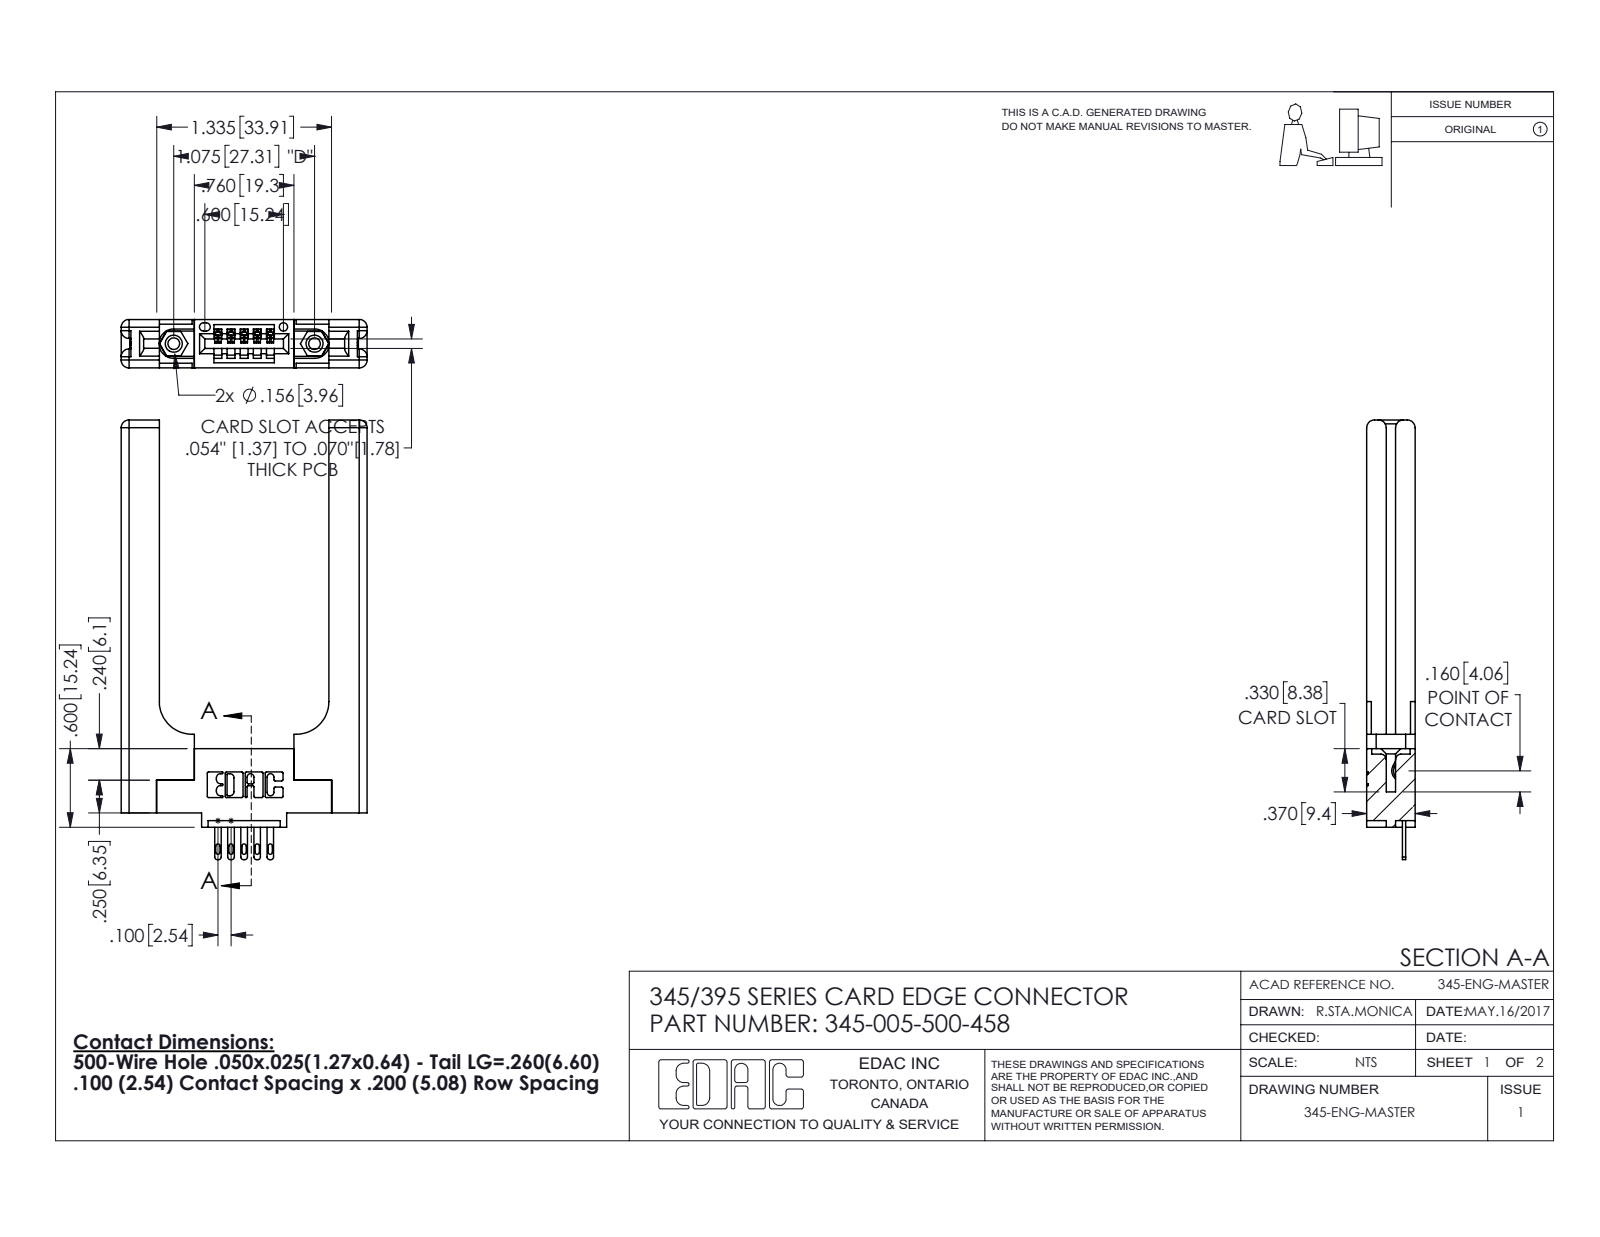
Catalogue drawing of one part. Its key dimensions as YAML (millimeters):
part_name: "345-250-001_345-250-001-102; 345 Part_0.110 Offset - 0.156 Dia-TH; 345-005-500-458; 345-292-001_345-293-100 (+1 more)"
step_written_by: "SolidWorks 2016 (CONFIG_CONTROL_DESIGN)"
units: millimeters
bodies: {solids: 10, faces: 656, planar: 402, cylindrical: 194, other: 60}
overall_size: [85.3, 47.7, 9.4]
volume: 12700
surface_area: 10430
round_holes:
  - {diameter: 2.3, count: 2}
  - {diameter: 3.2, count: 2}
  - {diameter: 4, count: 2}
  - {diameter: 1.6, count: 1}
round_bosses_or_shafts:
  - {diameter: 3.9, count: 2}
partial_cylinders:
  - {radius: 0.3, count: 22}
  - {radius: 1.5, count: 16}
  - {radius: 0.2, count: 10}
  - {radius: 0.4, count: 10}
  - {radius: 0.5, count: 10}
  - {radius: 0.2, count: 6}
  - {radius: 0.8, count: 6}
  - {radius: 0.7, count: 3}
face_to_face_distances: [9.4, 3.8, 5.6, 1.8, 32.9, 3.8, 2, 1.8, 7.6, 7.4]
hole_center_spacings: [6.9, 21.5, 27.3]
